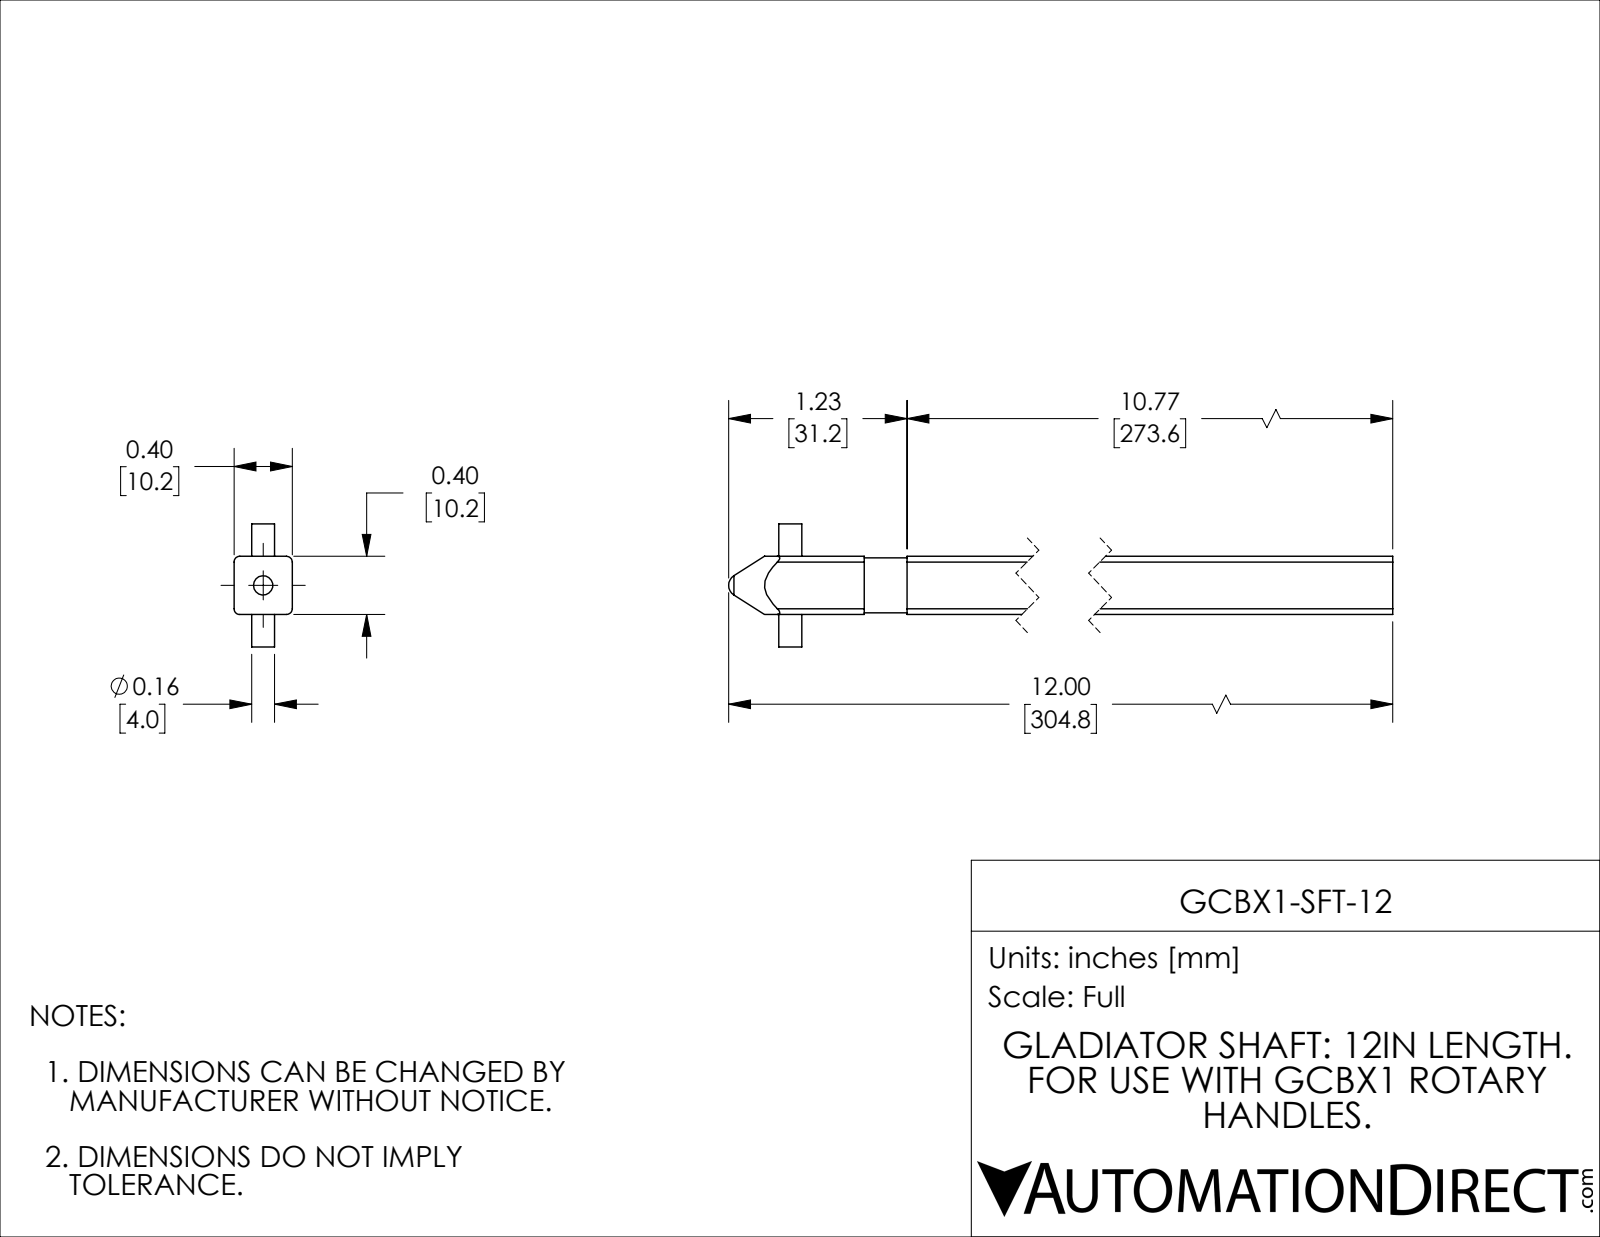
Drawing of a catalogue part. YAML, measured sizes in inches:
part_name: "GCBX1-SFT-12"
step_written_by: "SolidWorks 2021 (CONFIG_CONTROL_DESIGN)"
units: inches
bodies: {solids: 2, faces: 37, planar: 17, cylindrical: 17, other: 3}
overall_size: [12, 0.846, 0.4]
volume: 1.86
surface_area: 19.33
round_holes:
  - {diameter: 0.142, count: 1}
round_bosses_or_shafts:
  - {diameter: 0.378, count: 1}
  - {diameter: 0.157, count: 1}
partial_cylinders:
  - {radius: 0.039, count: 4}
face_to_face_distances: [0.4, 10.773, 11.068, 0.295, 0.194, 0.206, 0.223, 0.623, 0.846]
